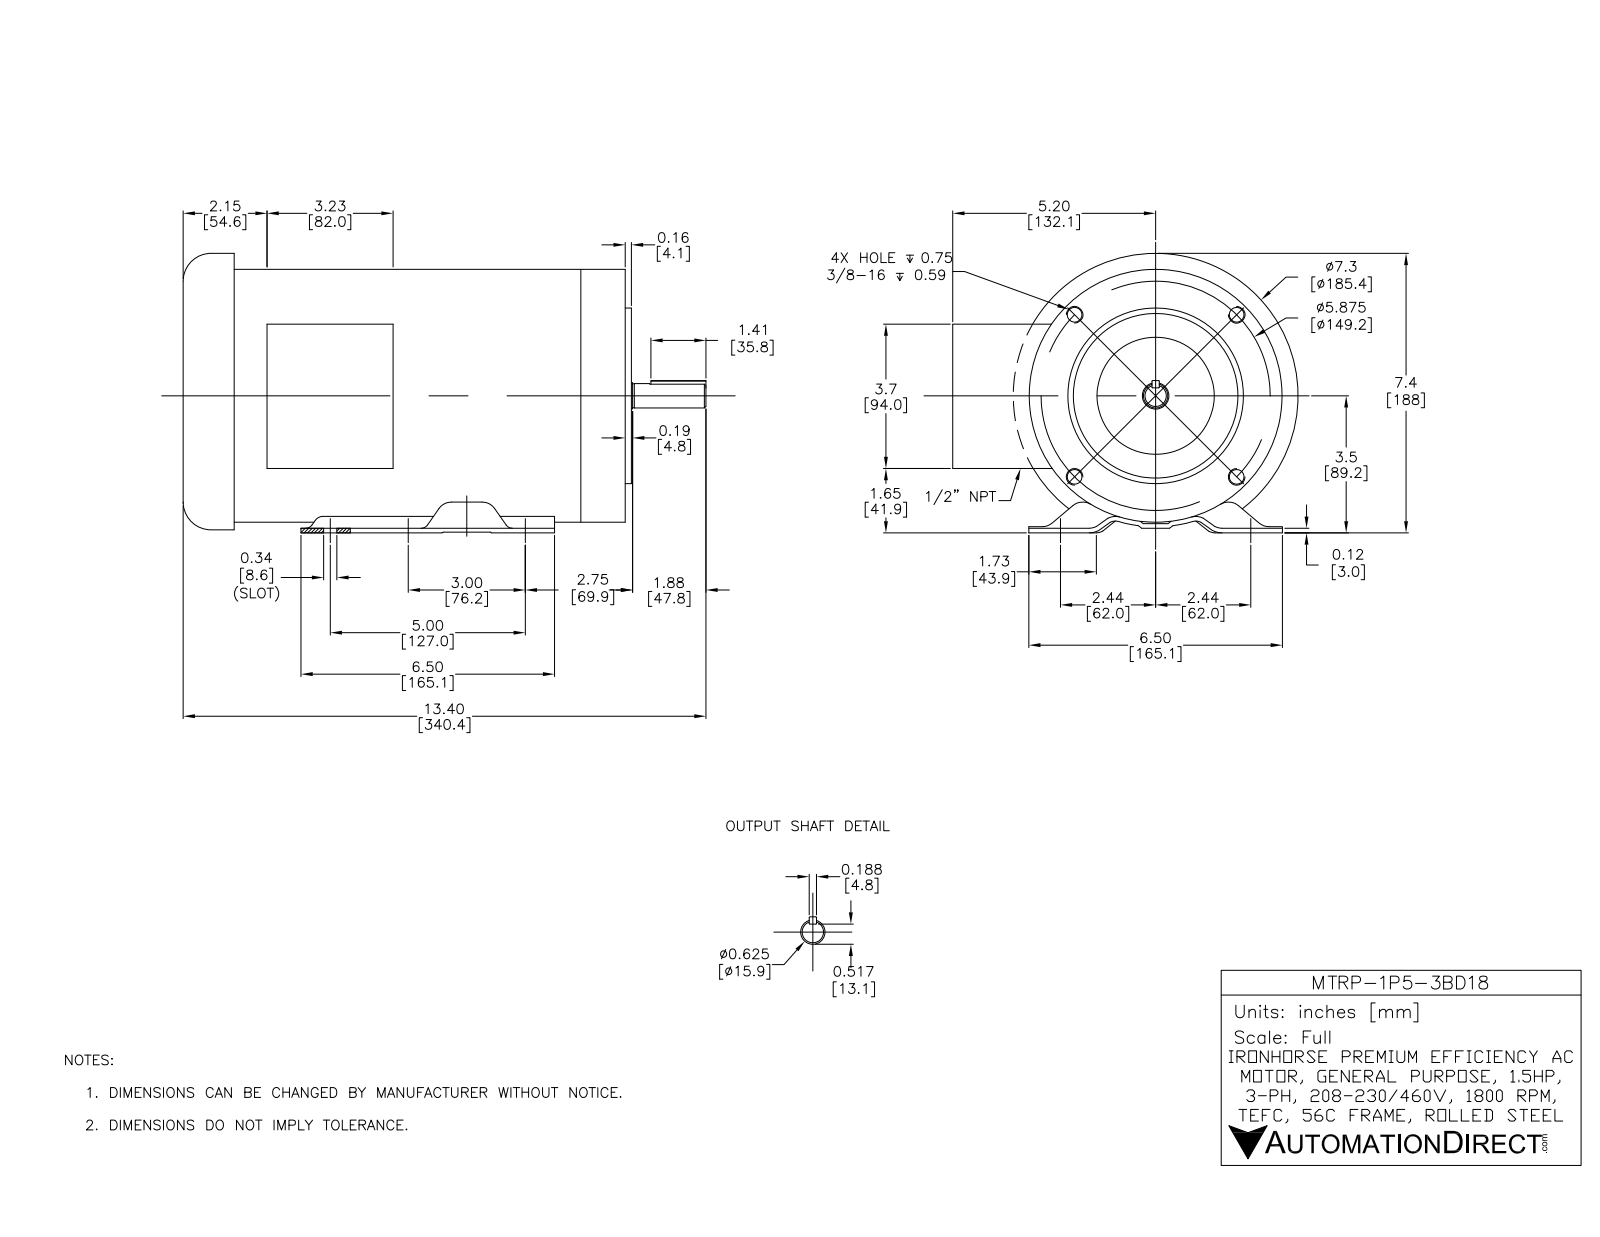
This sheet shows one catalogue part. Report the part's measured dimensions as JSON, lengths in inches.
{"part_name": "MTRP-1P5-3BD18", "step_written_by": "SolidWorks 2021 (AUTOMOTIVE_DESIGN)", "units": "inches", "bodies": {"solids": 39, "faces": 3602, "planar": 797, "cylindrical": 1141, "other": 1664}, "overall_size": [13.209, 8.938, 7.234], "volume_in3": 46.77, "surface_area_in2": 1021, "round_holes": [[0.197, 12], [0.219, 9], [0.276, 8], [0.217, 6], [0.273, 6], [0.344, 6], [0.136, 5], [0.15, 4], [0.177, 4], [0.313, 4], [0.067, 2], [0.134, 2]], "round_bosses_or_shafts": [[0.164, 9], [0.414, 6], [0.348, 6], [0.25, 6], [0.19, 6], [0.348, 3], [7.185, 1], [6.457, 1]], "partial_cylinders_radius": [[0.02, 204], [0.118, 123], [0.079, 43], [0.039, 38], [0.157, 32], [0.138, 26], [0.276, 19], [0.172, 12]], "face_to_face_distances": [0.118, 0.039, 0.063, 11.142, 11.102, 3.559, 0.079, 3.087, 0.047, 0.098], "hole_center_spacings": [4.221, 3.031, 0.094, 2.32, 2.409, 2.937, 2.979, 3.748]}
